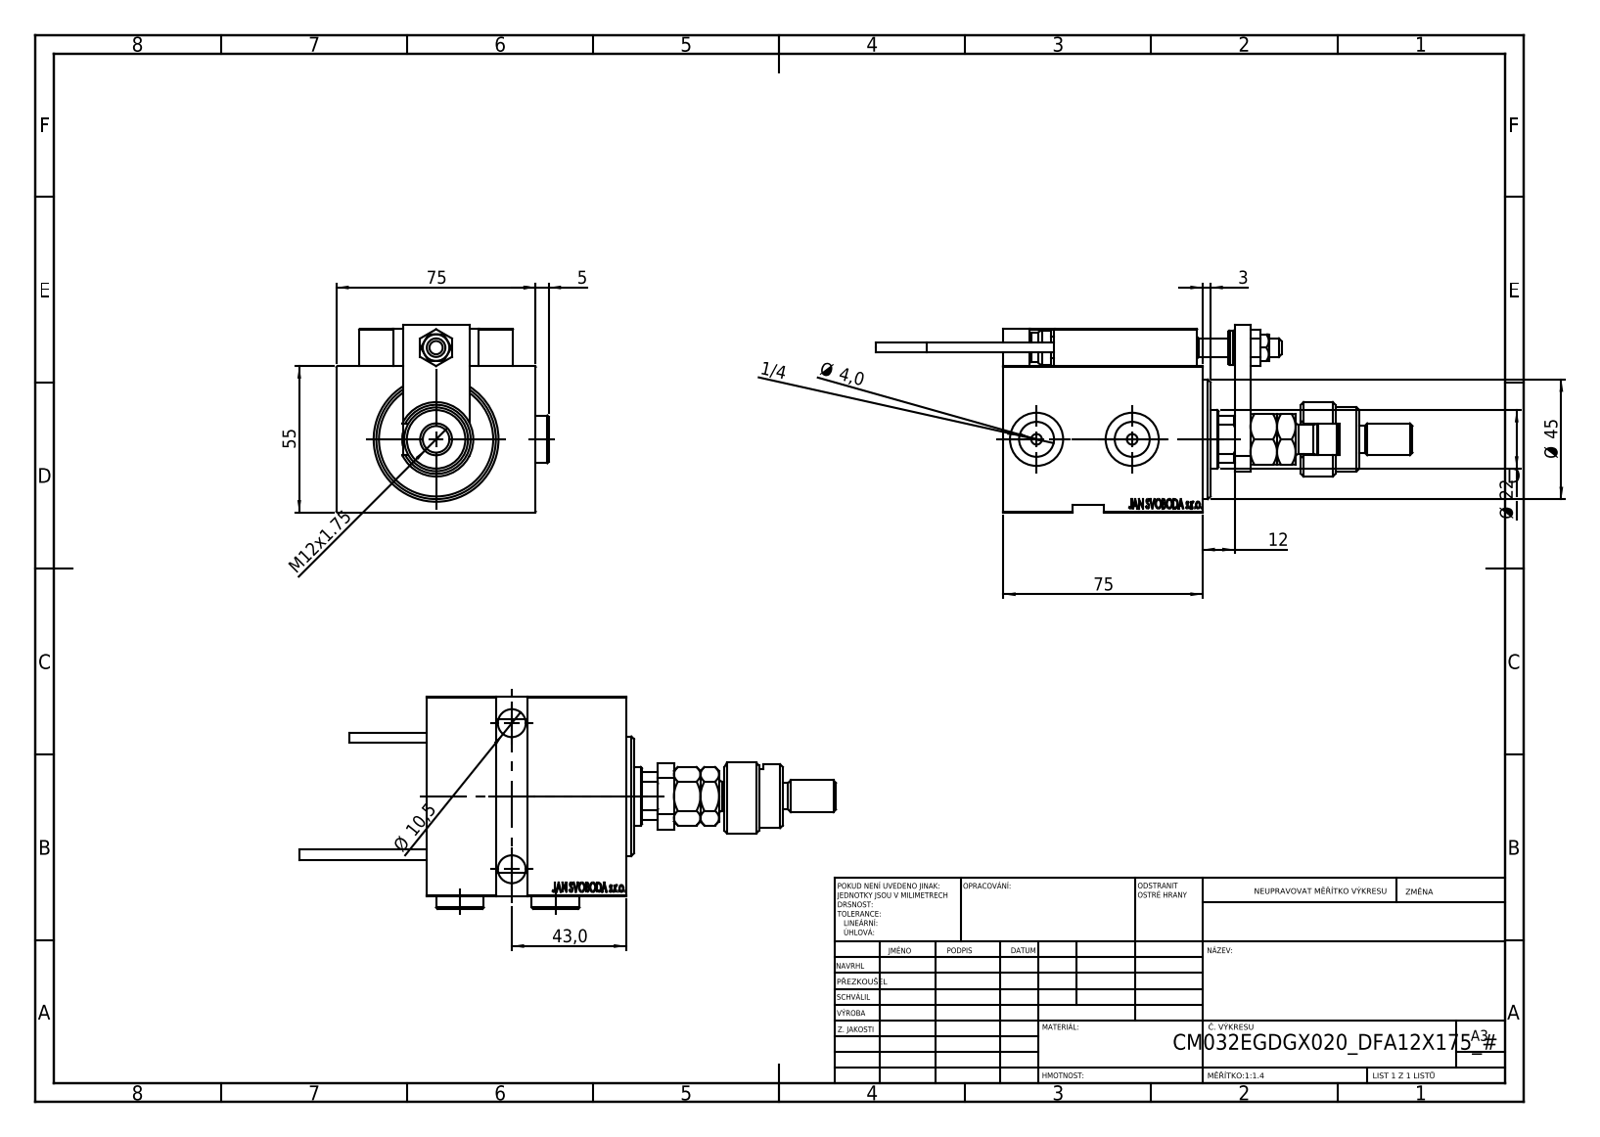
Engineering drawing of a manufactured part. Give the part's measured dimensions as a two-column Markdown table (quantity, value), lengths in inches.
| quantity | value |
| --- | --- |
| part name | ALLEN BOLT D5; SWITCH X; ALLEN BOLT D8; V450CM_E_VCP (+7 more) |
| STEP written by | SolidWorks 2019 (CONFIG_CONTROL_DESIGN) |
| units | inches |
| bodies | 28 solids, 1421 faces (631 planar, 201 cylindrical, 589 other) |
| overall size | 7.953 × 3.146 × 2.776 |
| volume | 21.38 in³ |
| surface area | 135.6 in² |
| round holes (diameter × count) | 0.157 × 6, 0.315 × 5, 0.126 × 4, 0.413 × 3, 0.65 × 3, 0.197 × 2, 0.518 × 2, 0.787 × 2, 0.276 × 1, 0.866 × 1, 1.004 × 1, 1.26 × 1 |
| round bosses / shafts (diameter × count) | 0.709 × 3, 0.433 × 2, 0.197 × 2, 0.15 × 2, 1.339 × 1, 1.102 × 1, 0.945 × 1, 0.512 × 1 |
| partial cylindrical surfaces (radius × count) | 0.012 × 30, 0.118 × 2, 0.384 × 1, 0.413 × 1 |
| main face-to-face distances | 2.953, 2.165, 0.472, 0.118, 0.551, 0.394, 0.197, 0.984, 0.709, 2.717 |
| hole center spacings | 0.448, 0.787, 1.066, 1.165, 1.169, 1.267, 1.371, 1.42 |
